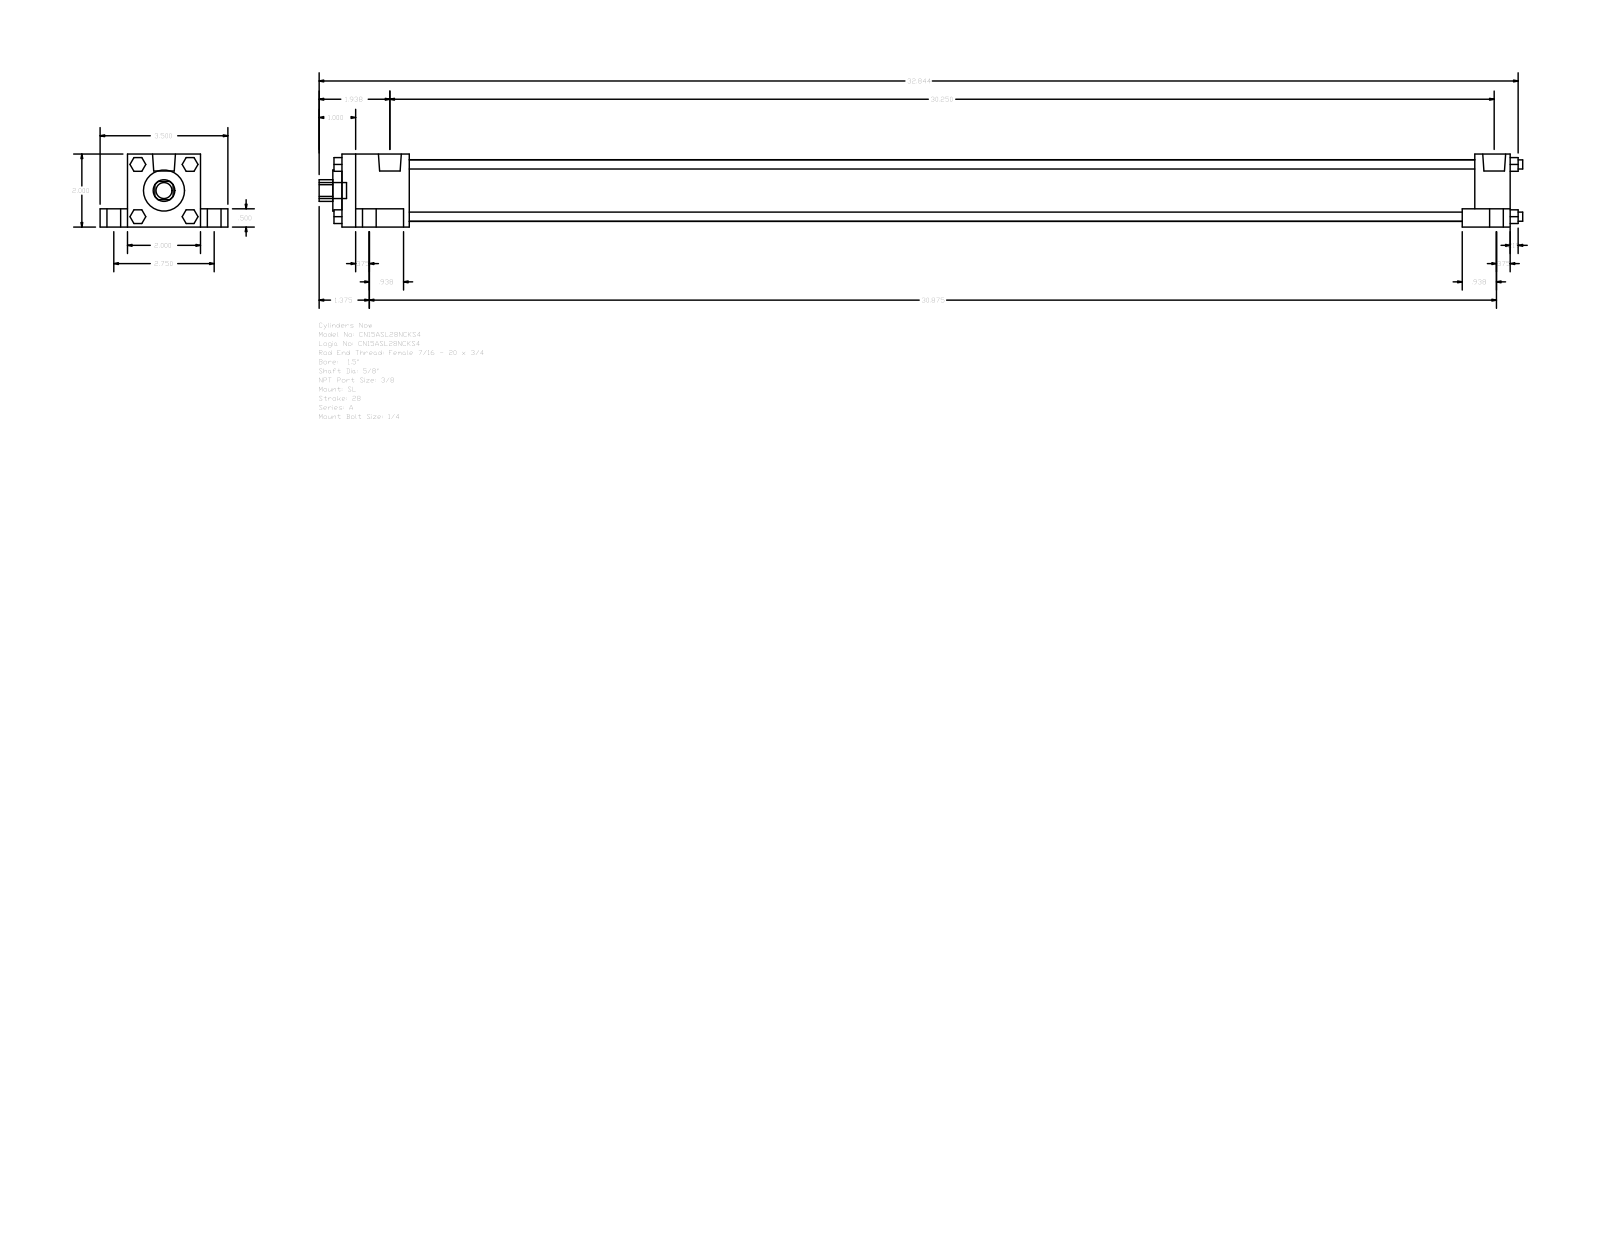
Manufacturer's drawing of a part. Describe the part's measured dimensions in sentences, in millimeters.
The part is named "A_SL__0150_0.625". Its 3-D file was written by "GSSL Pune (CONFIG_CONTROL_DESIGN)". It is 0 solids with 148 faces: 112 planar, 36 cylindrical and 0 other. Overall it measures 837.41 by 88.9 by 50.8 millimeters. Round holes: 1 of diameter 15.88, 1 of diameter 28.57, 1 of diameter 42.93. Round bosses or shafts: 4 of diameter 15.88, 4 of diameter 9.53, 4 of diameter 6.35, 4 of diameter 5.56, 2 of diameter 15.93, 1 of diameter 11.11. Partial cylindrical surfaces (rounded edges, fillets, slot ends): 1 of radius 7.54. The main face-to-face distances are 50.8, 19.05, 12.7, 38.1, 69.85, 812.79, 9.52, 788.19, 24.6, 46.83.
